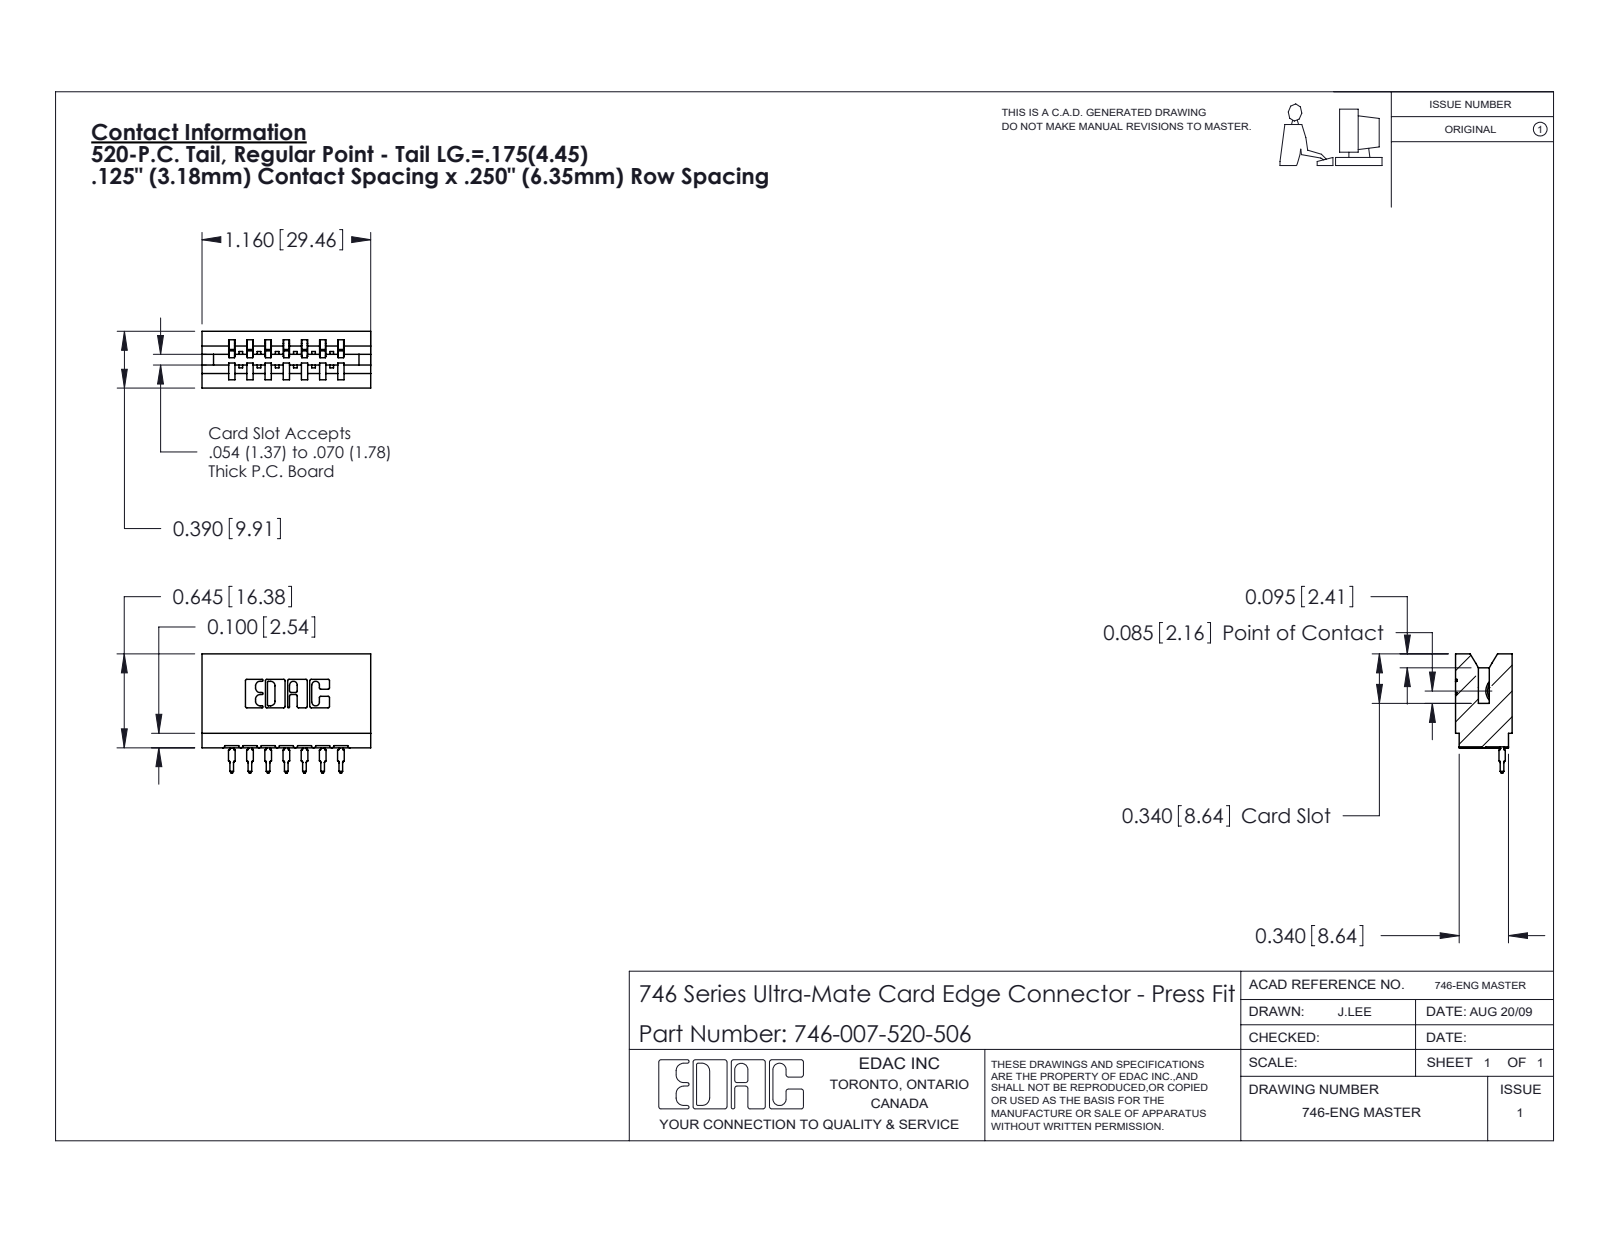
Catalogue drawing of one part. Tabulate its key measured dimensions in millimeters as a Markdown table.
| quantity | value |
| --- | --- |
| part name | 746-007-520-506; 746 Part_.340 Slot Depth - 06; 746-292-001_520 |
| STEP written by | SolidWorks 2020 (CONFIG_CONTROL_DESIGN) |
| units | millimeters |
| bodies | 8 solids, 854 faces (497 planar, 175 cylindrical, 182 other) |
| overall size | 29.5 × 20.8 × 9.9 |
| volume | 3 490 mm³ |
| surface area | 4 130 mm² |
| partial cylindrical surfaces (radius × count) | 0.3 × 22, 0.5 × 14, 0.4 × 8, 0.2 × 6, 0.8 × 6, 0.1 × 4, 0.3 × 4, 0.7 × 3 |
| main face-to-face distances | 6.4, 1.1, 8.5, 3.2, 12.7, 3.2, 7.4, 5.3, 1.4, 9.9 |
